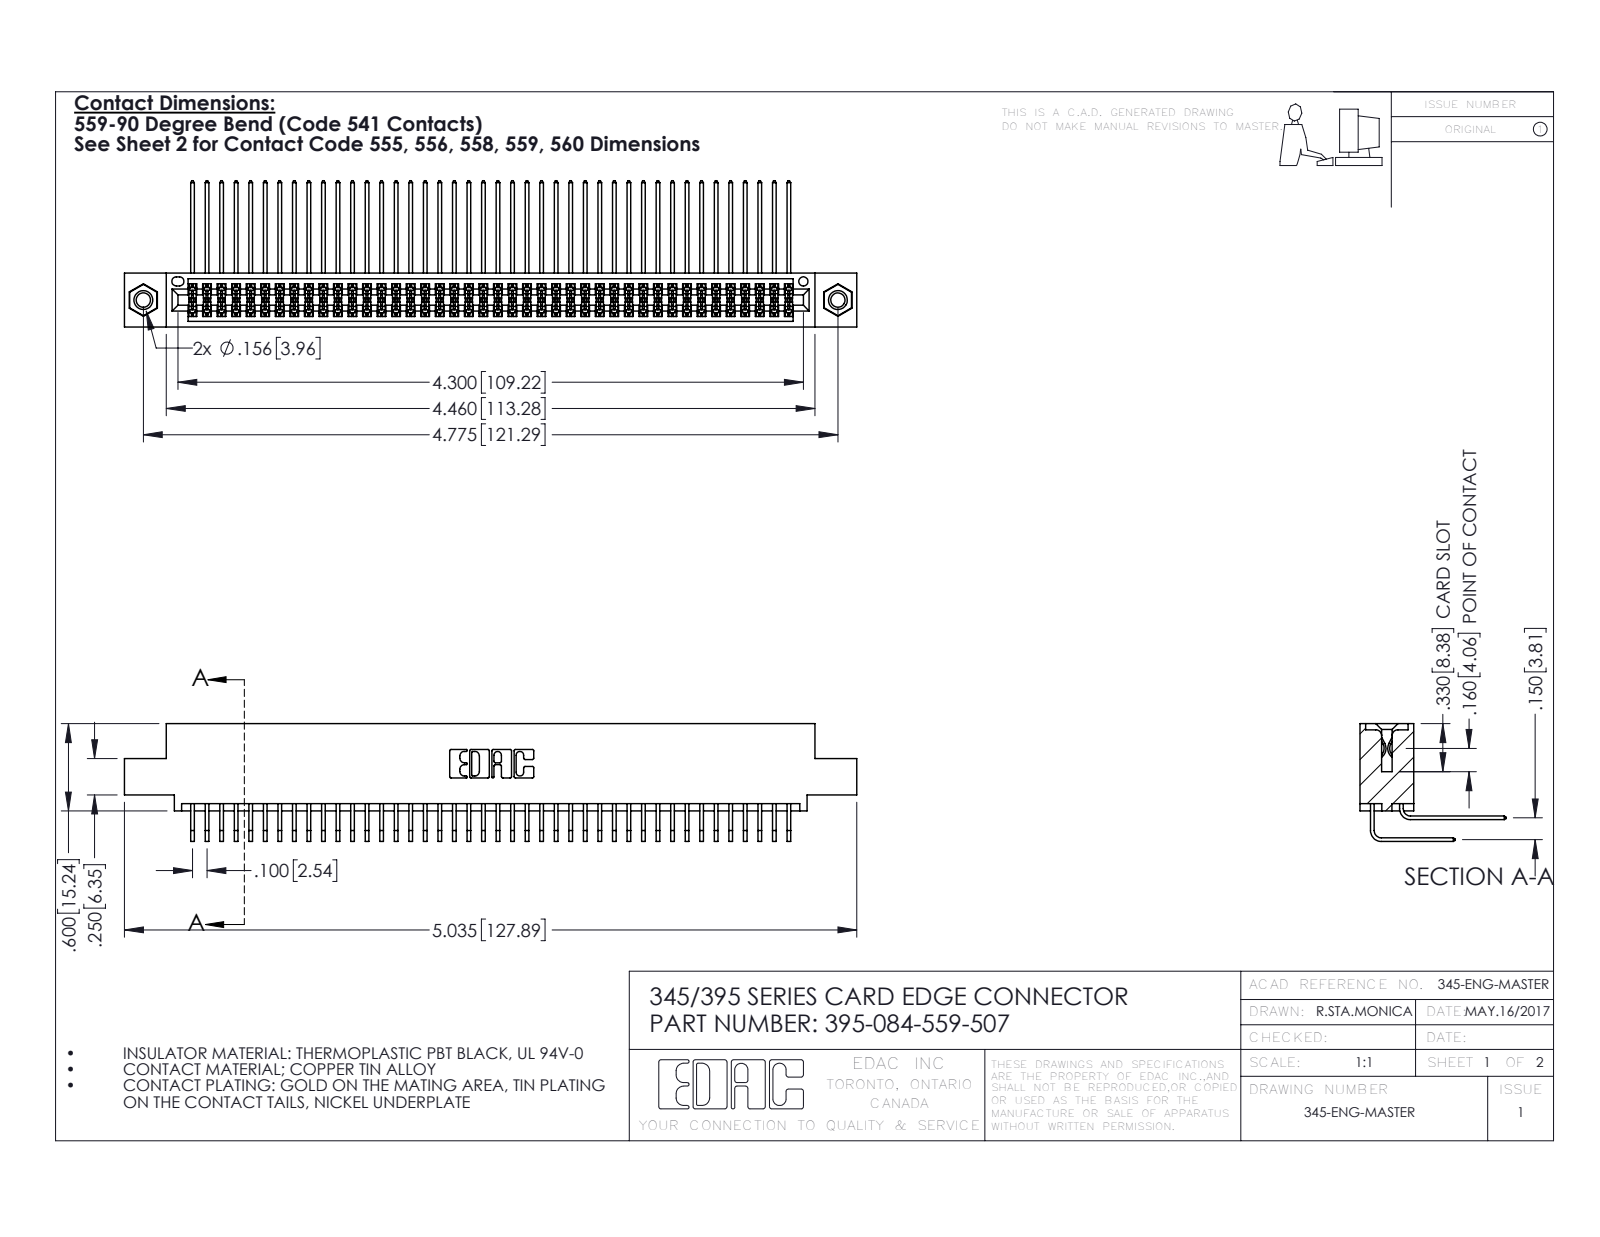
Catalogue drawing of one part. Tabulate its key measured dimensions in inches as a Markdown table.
| quantity | value |
| --- | --- |
| part name | 345-292-001_559 Tail - 2; 395-084-559-507; 345 Part_0.110 Offset - 0.156 Dia-TI; 345-250-001_345-250-005-103 (+1 more) |
| STEP written by | SolidWorks 2016 (CONFIG_CONTROL_DESIGN) |
| units | inches |
| bodies | 87 solids, 4558 faces (3056 planar, 1486 cylindrical, 16 other) |
| overall size | 5.035 × 1.005 × 0.809 |
| volume | 0.782 in³ |
| surface area | 33.09 in² |
| round holes (diameter × count) | 0.098 × 2, 0.125 × 2, 0.156 × 2, 0.064 × 1 |
| round bosses / shafts (diameter × count) | 0.155 × 2 |
| partial cylindrical surfaces (radius × count) | 0.006 × 126, 0.01 × 22, 0.007 × 6, 0.031 × 6, 0.026 × 3, 0.014 × 2, 0.019 × 2, 0.022 × 2 |
| main face-to-face distances | 0.072, 0.298, 0.2, 0.37, 0.098, 0.272, 0.025, 0.225, 0.175, 0.15 |
| hole center spacings | 0.27, 4.539, 4.775 |
